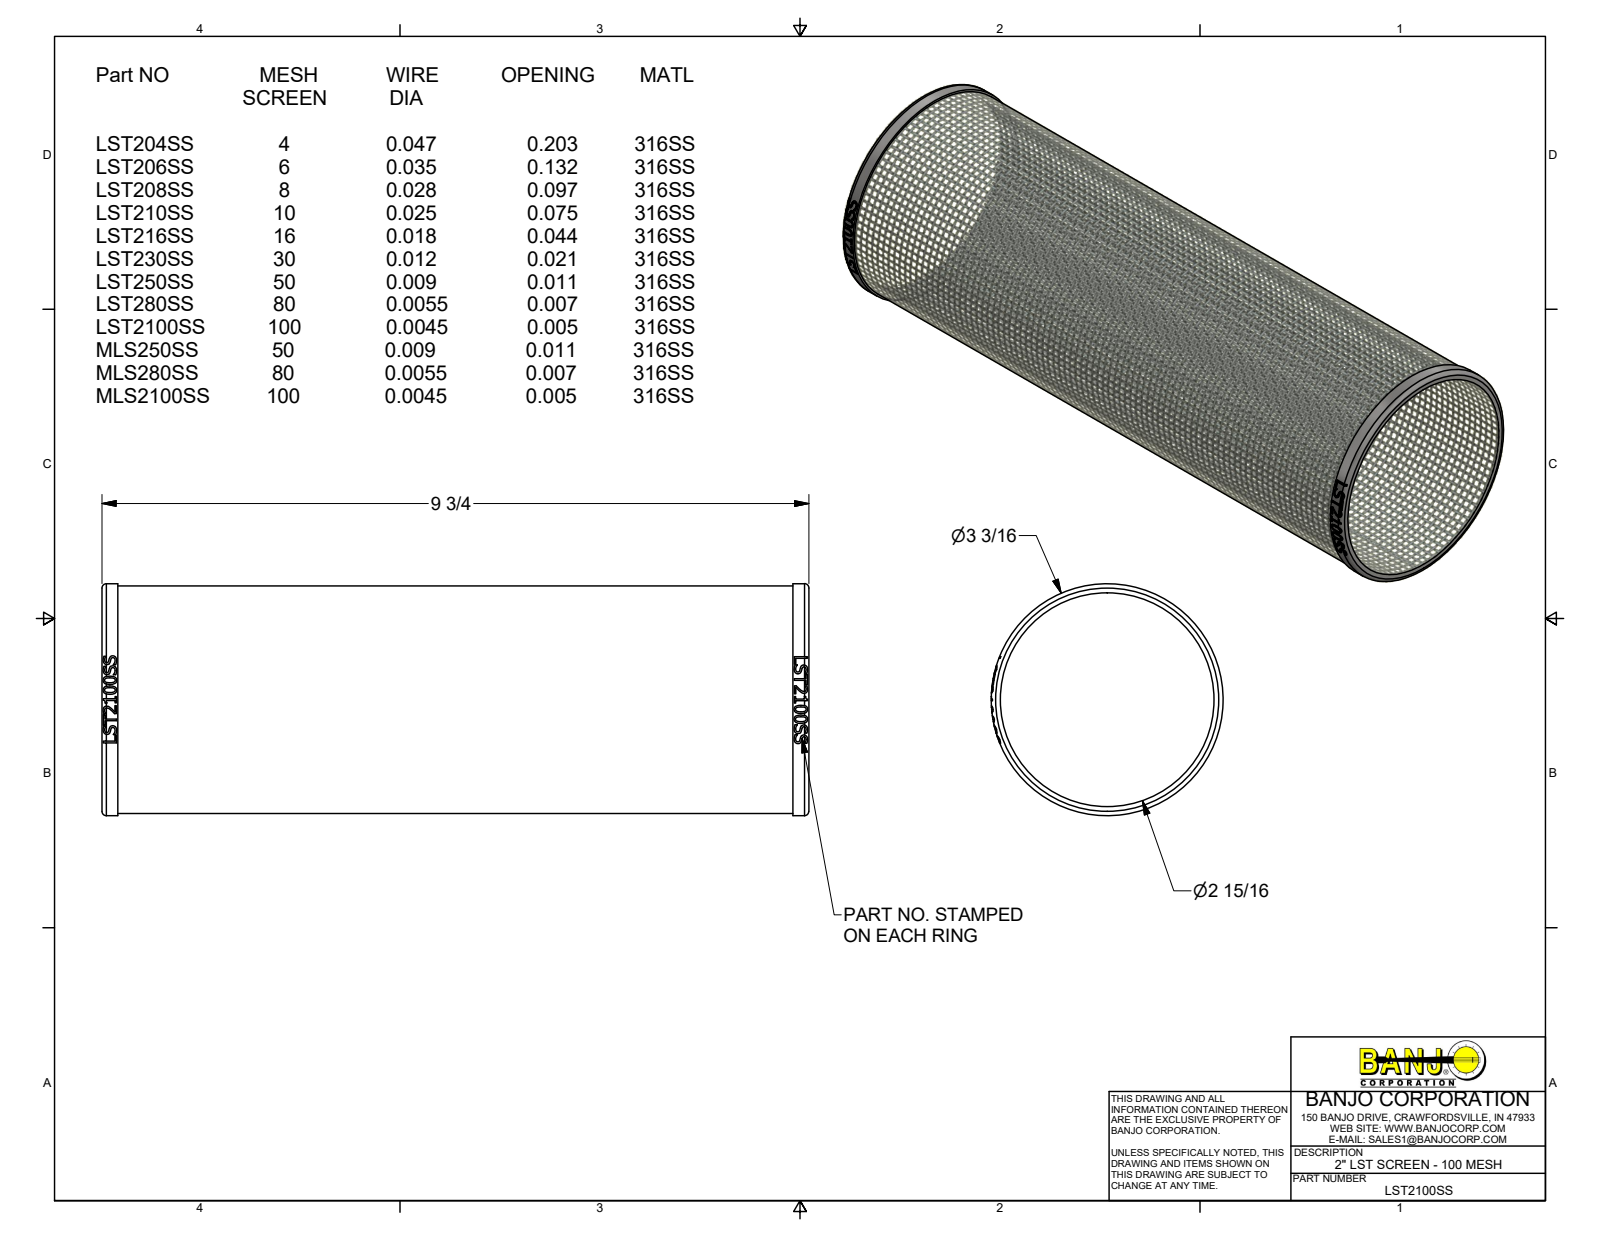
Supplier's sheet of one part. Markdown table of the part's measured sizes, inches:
| quantity | value |
| --- | --- |
| part name | LST2100SS |
| STEP written by | Autodesk Inventor 2017 (AUTOMOTIVE_DESIGN) |
| units | inches |
| bodies | 1 solid, 284 faces (88 planar, 26 cylindrical, 170 other) |
| overall size | 9.72 × 3.188 × 3.188 |
| volume | 8.933 in³ |
| surface area | 188 in² |
| round holes (diameter × count) | 2.937 × 1 |
| round bosses / shafts (diameter × count) | 3.188 × 1, 3.128 × 1 |
| partial cylindrical surfaces (radius × count) | 1.574 × 1 |
| main face-to-face distances | 9.72, 9.501, 0.219, 9.282, 0.279, 0.019, 0.2, 0.579, 0.02, 9.52 |
